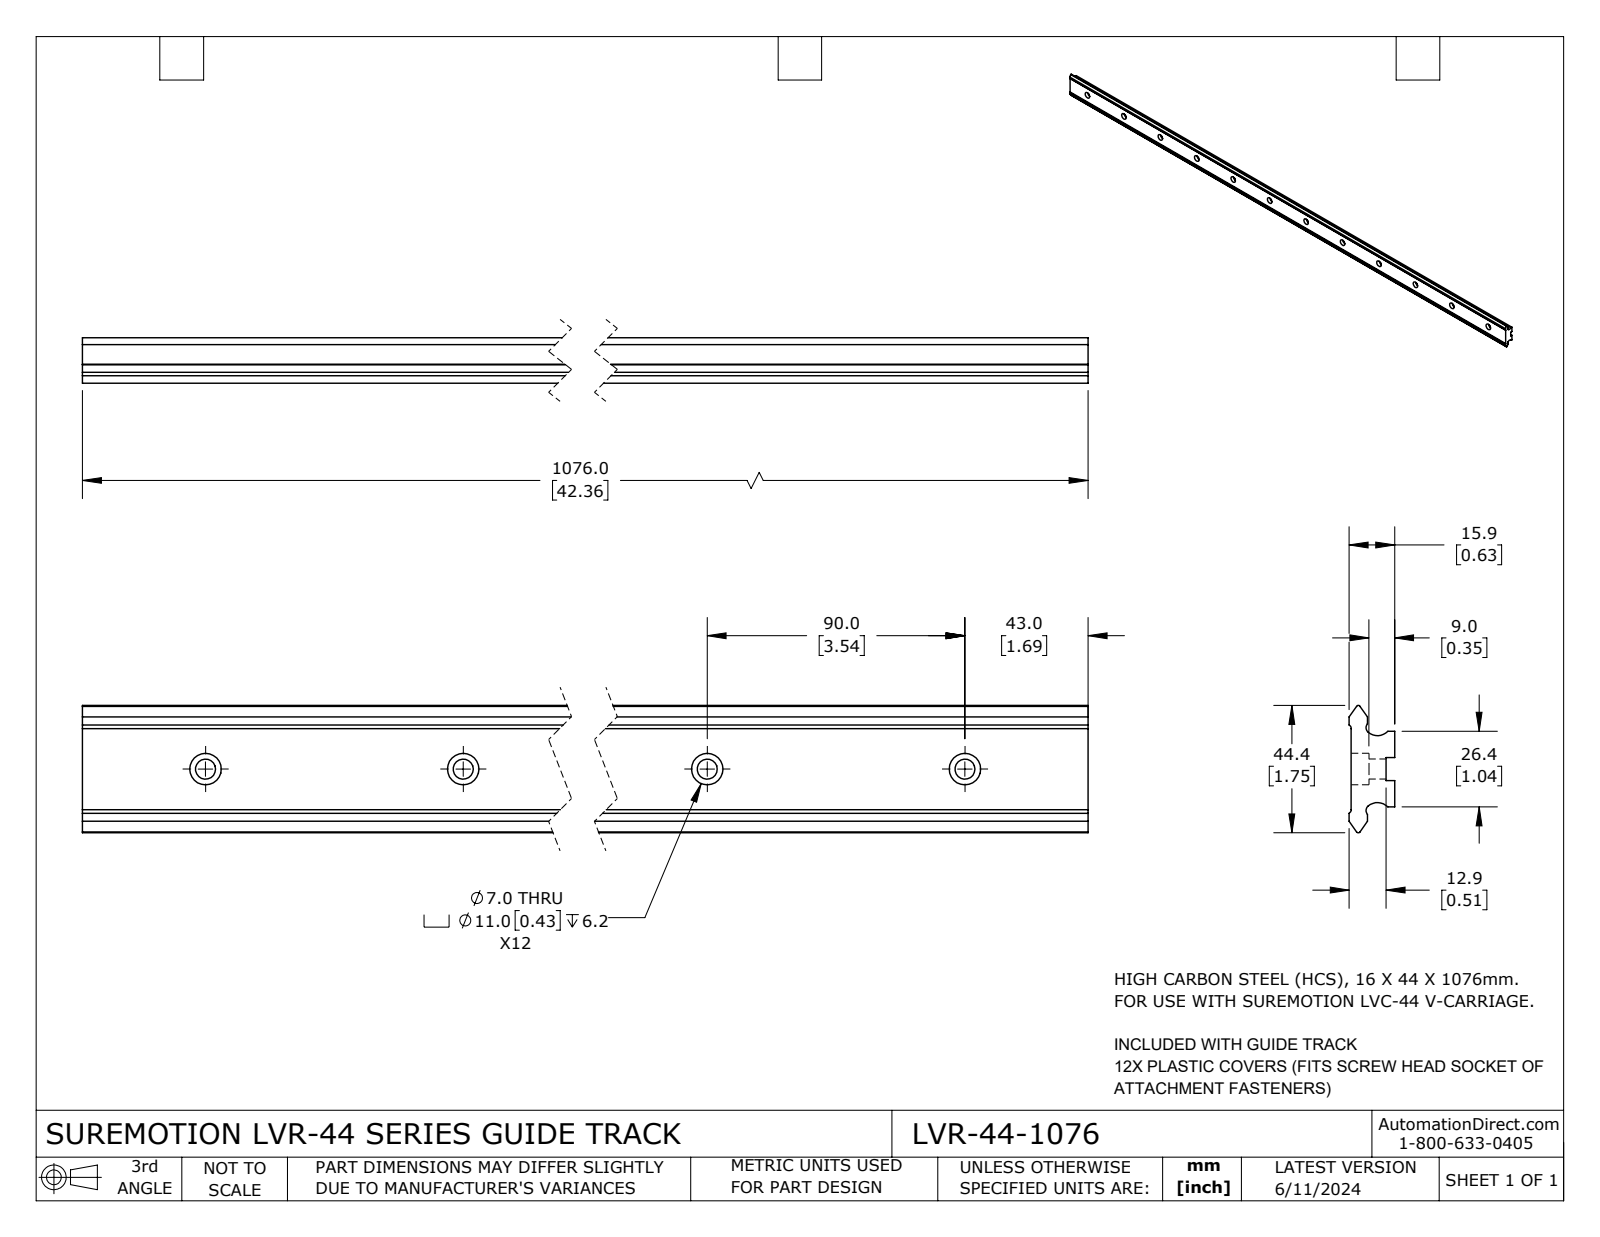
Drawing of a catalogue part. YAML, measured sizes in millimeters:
part_name: "LVR-44-1076"
step_written_by: "SolidWorks 2023 (CONFIG_CONTROL_DESIGN)"
units: millimeters
bodies: {solids: 1, faces: 88, planar: 30, cylindrical: 58, other: 0}
overall_size: [1076, 44.45, 15.91]
volume: 475281
surface_area: 134892
round_holes:
  - {diameter: 7, count: 12}
  - {diameter: 11, count: 12}
partial_cylinders:
  - {radius: 0.76, count: 2}
  - {radius: 1.5, count: 2}
  - {radius: 2.13, count: 2}
  - {radius: 4.98, count: 2}
face_to_face_distances: [15.2, 26.16, 3, 12.2, 15.91, 12.91, 0.71, 9.2, 17.2, 9.48]
hole_center_spacings: [90, 180, 270, 360, 450, 540, 630, 720]
